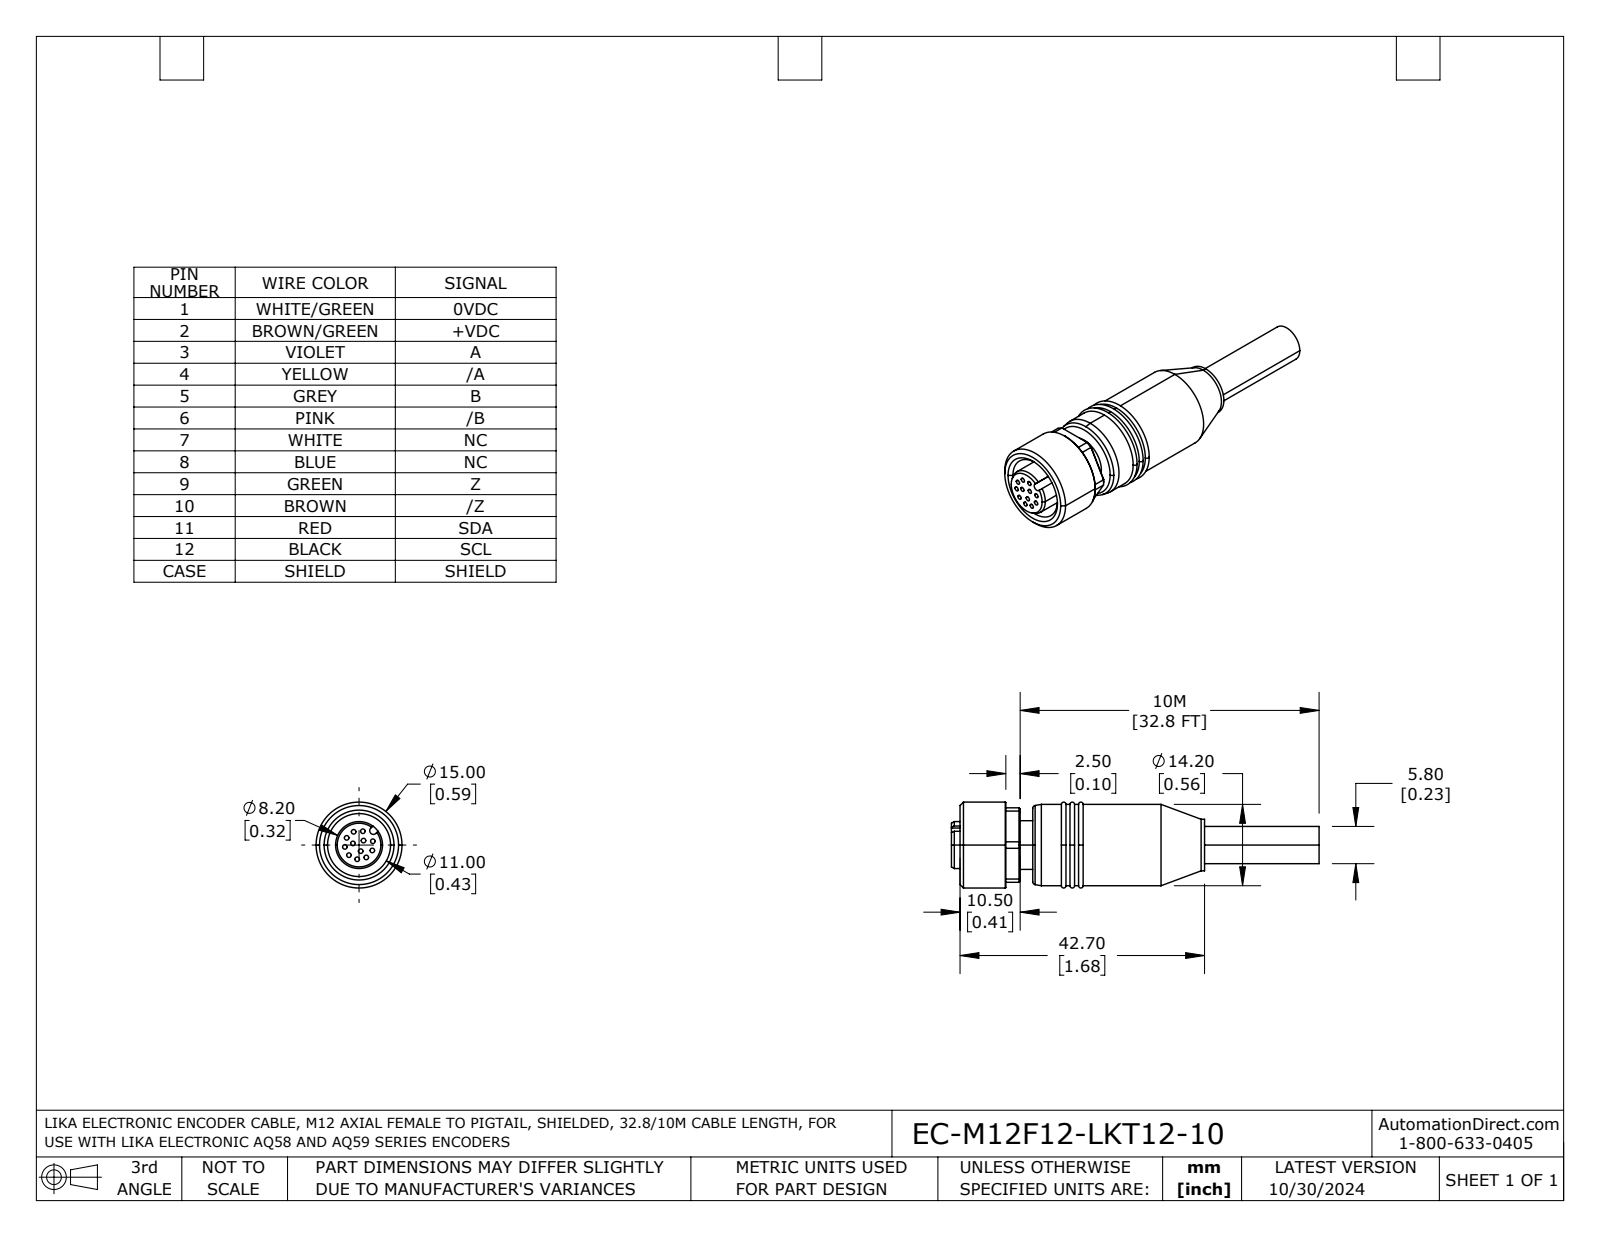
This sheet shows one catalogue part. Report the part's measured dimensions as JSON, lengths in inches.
{"part_name": "EC-M12F12-LKT12-10", "step_written_by": "SolidWorks 2021 (AUTOMOTIVE_DESIGN)", "units": "inches", "bodies": {"solids": 1, "faces": 146, "planar": 35, "cylindrical": 73, "other": 38}, "overall_size": [2.528, 0.591, 0.591], "volume_in3": 0.404, "surface_area_in2": 5.314, "round_holes": [[0.031, 12], [0.433, 1]], "round_bosses_or_shafts": [[0.591, 1], [0.559, 1], [0.354, 1], [0.335, 1], [0.323, 1], [0.256, 1]], "partial_cylinders_radius": [[0.026, 1], [0.283, 1]], "face_to_face_distances": [0.087, 0.512, 0.205, 0.118, 0.559, 0.472, 0.354, 1.969, 2.055, 2.173], "hole_center_spacings": [0.098, 0.063, 0.164, 0.12, 0.191, 0.196, 0.043, 0.181]}
